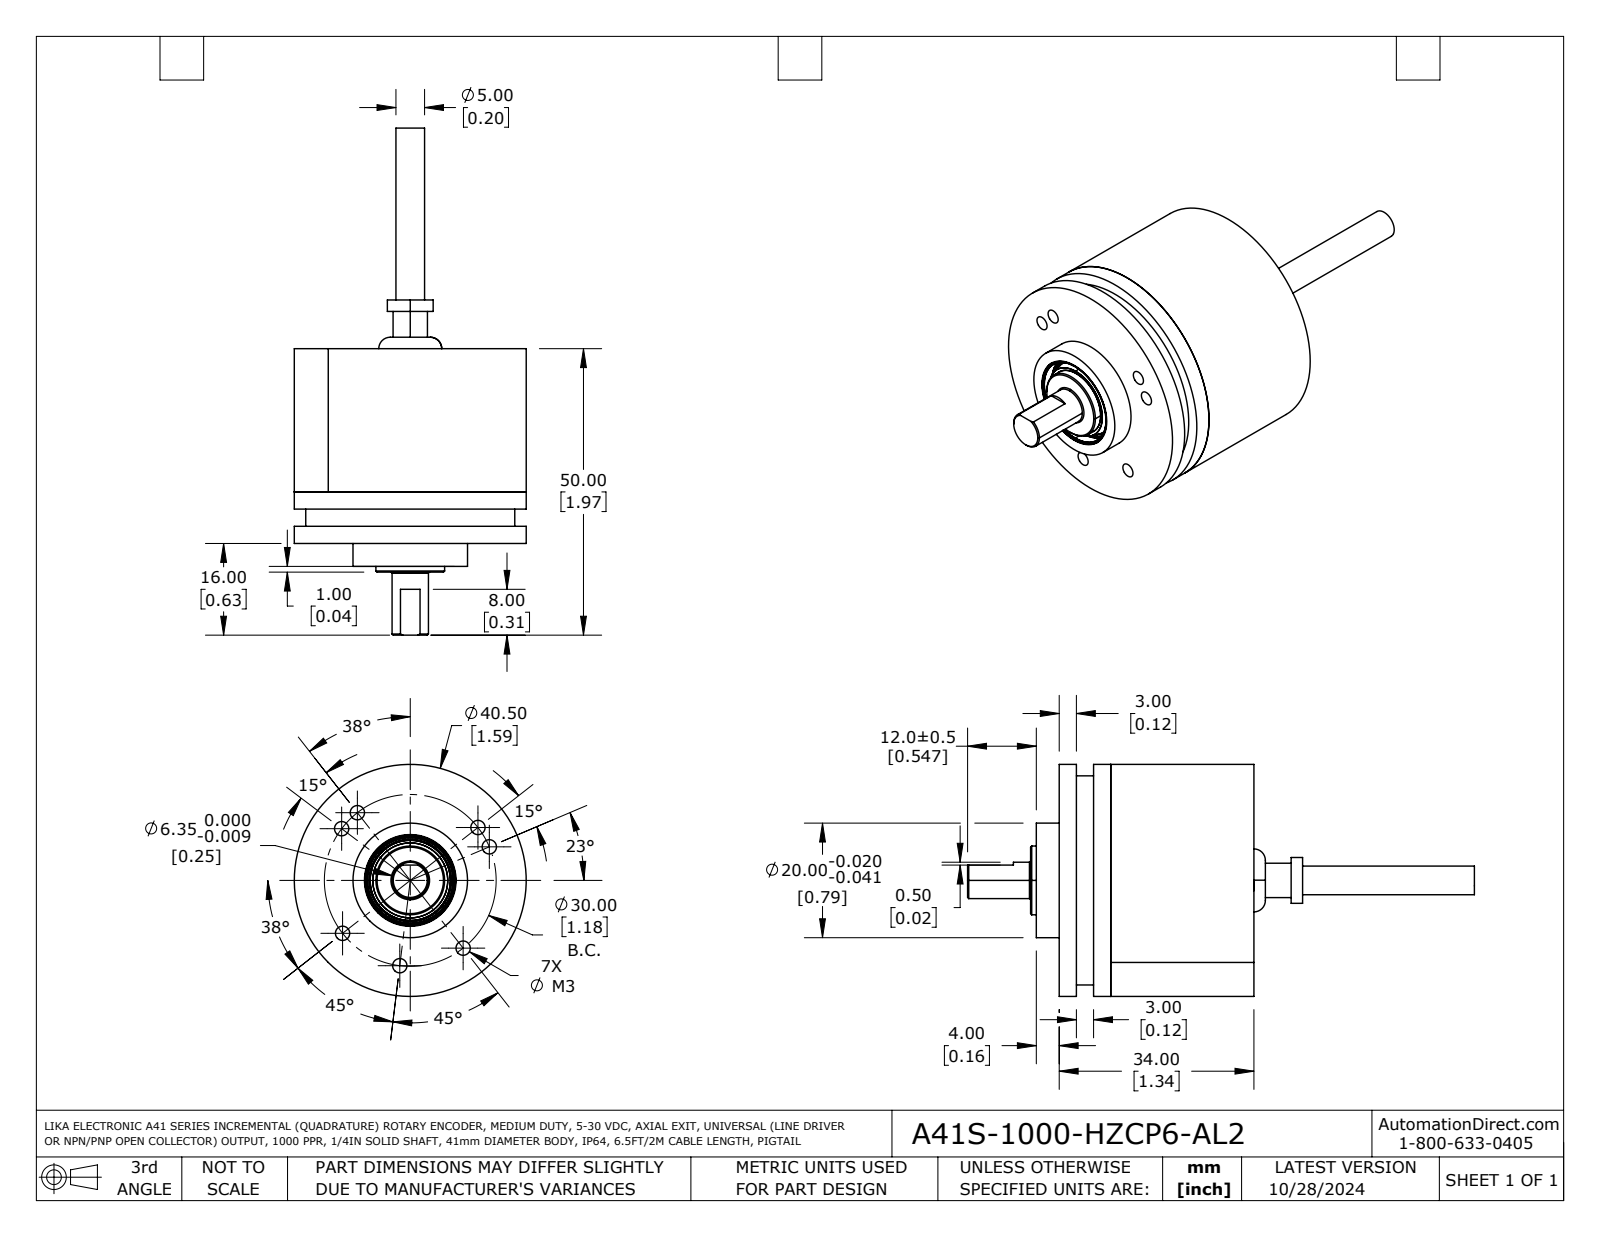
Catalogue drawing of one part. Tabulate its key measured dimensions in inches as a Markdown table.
| quantity | value |
| --- | --- |
| part name | A41S-1000-HZCP6-AL2 |
| STEP written by | SolidWorks 2021 (AUTOMOTIVE_DESIGN) |
| units | inches |
| bodies | 11 solids, 422 faces (76 planar, 145 cylindrical, 201 other) |
| overall size | 3.484 × 1.594 × 1.594 |
| volume | 1.175 in³ |
| surface area | 28.29 in² |
| round holes (diameter × count) | 0.063 × 7, 0.098 × 7, 0.157 × 3, 0.087 × 2, 0.169 × 1, 0.295 × 1, 0.512 × 1, 0.602 × 1, 0.612 × 1, 0.63 × 1, 1.516 × 1 |
| round bosses / shafts (diameter × count) | 0.079 × 2, 1.594 × 1, 1.496 × 1, 1.457 × 1, 1.437 × 1, 0.787 × 1, 0.472 × 1, 0.315 × 1 |
| partial cylindrical surfaces (radius × count) | 0.039 × 14, 0.007 × 6, 0.008 × 2 |
| main face-to-face distances | 0.118, 1.339, 0.433, 0.906, 1.22, 0.079, 0.866, 0.984, 0.787, 0.039 |
| hole center spacings | 0.591, 0.669, 0.835, 0.11, 0.118, 0.837, 0.945, 1.257 |
